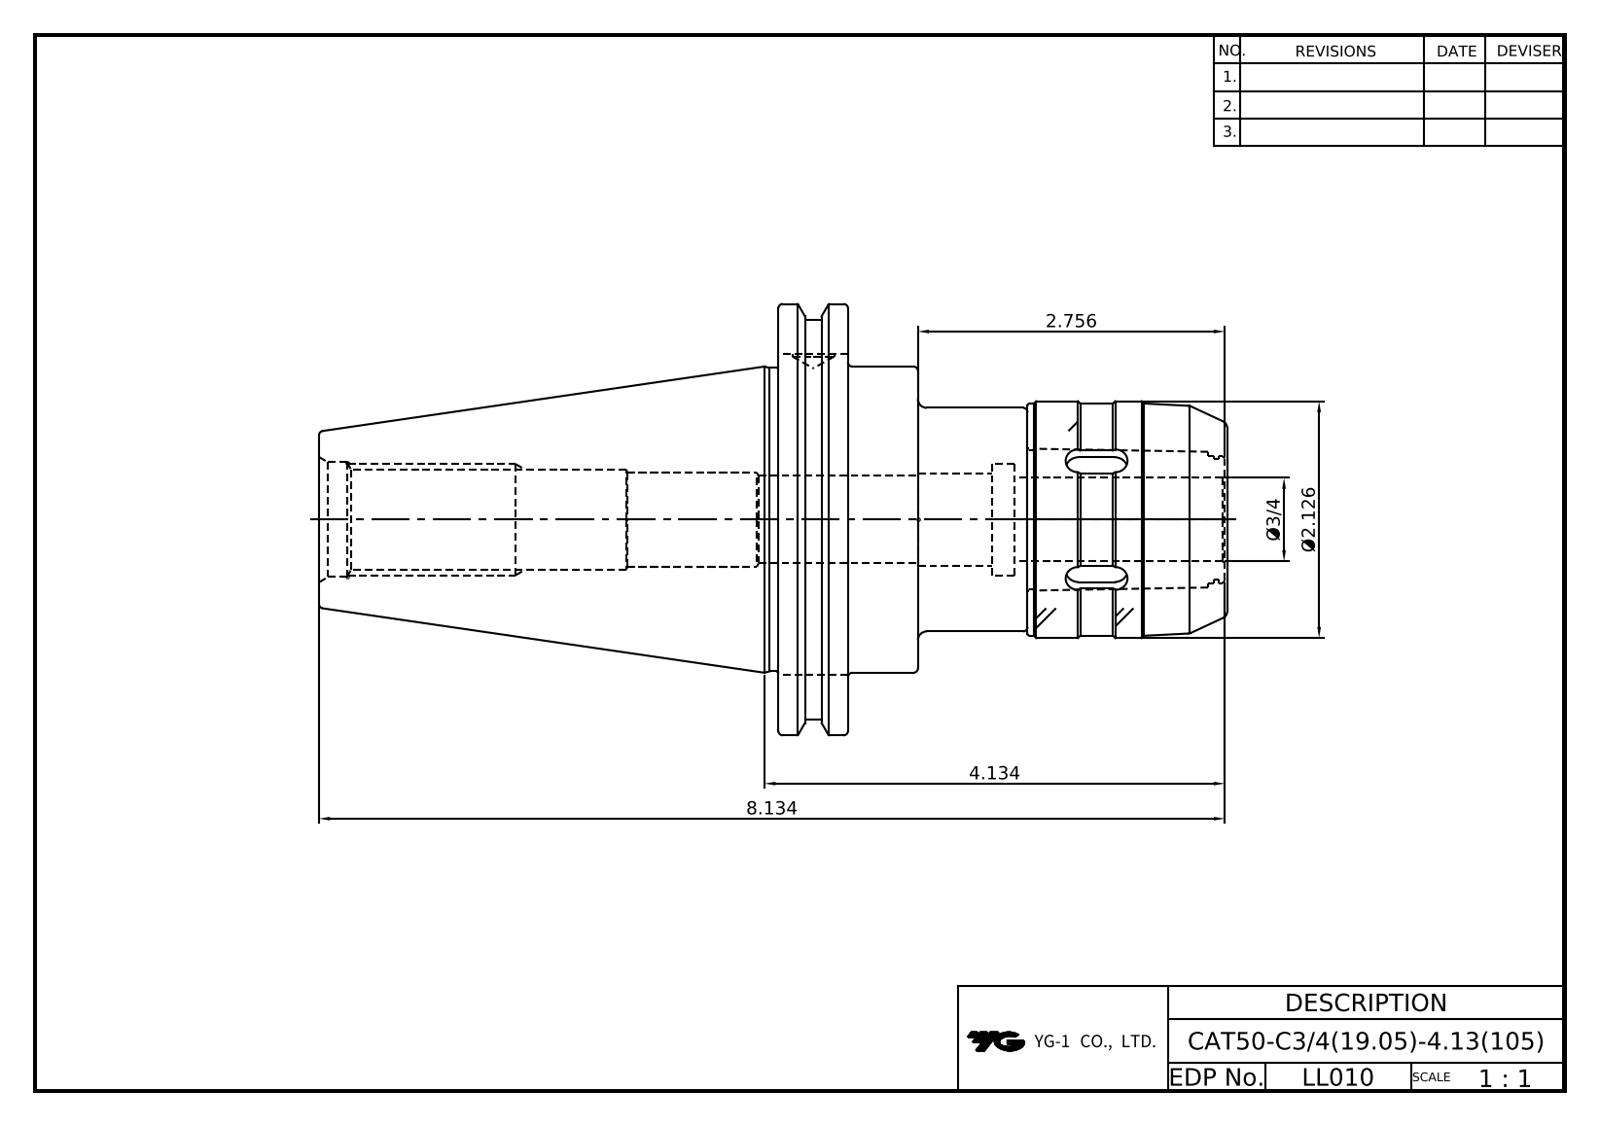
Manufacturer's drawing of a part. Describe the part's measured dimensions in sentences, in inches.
The part is named "LL010-CAT50-C19_05-105; C20_CAP; LL010-CAT50-C19_05-105_ASM". Its 3-D file was written by "PRO/ENGINEER BY PARAMETRIC TECHNOLOGY CORPORATION, 2012130 (CONFIG_CONTROL_DESIGN)". It is 2 solids with 221 faces: 49 planar, 72 cylindrical and 100 other. Overall it measures 8.154 by 3.874 by 3.737 inches. Its volume is 30.06 cubic inches and its surface area 119.7 square inches. Round holes: 1 of diameter 0.375, 1 of diameter 0.75, 1 of diameter 0.787, 1 of diameter 0.827, 1 of diameter 0.846, 1 of diameter 0.898, 1 of diameter 1.008, 1 of diameter 1.031, 1 of diameter 1.539, 1 of diameter 1.614. Round bosses or shafts: 1 of diameter 3.874, 1 of diameter 3.594, 1 of diameter 2.75, 1 of diameter 2.726, 1 of diameter 2.126, 1 of diameter 2.087, 1 of diameter 2.008, 1 of diameter 1.299. Partial cylindrical surfaces (rounded edges, fillets, slot ends): 10 of radius 0.118. The main face-to-face distances are 0.625, 2.237, 1.612, 0.628, 1.253, 0.984, 4.125, 4.75, 5.378, 6.362.
